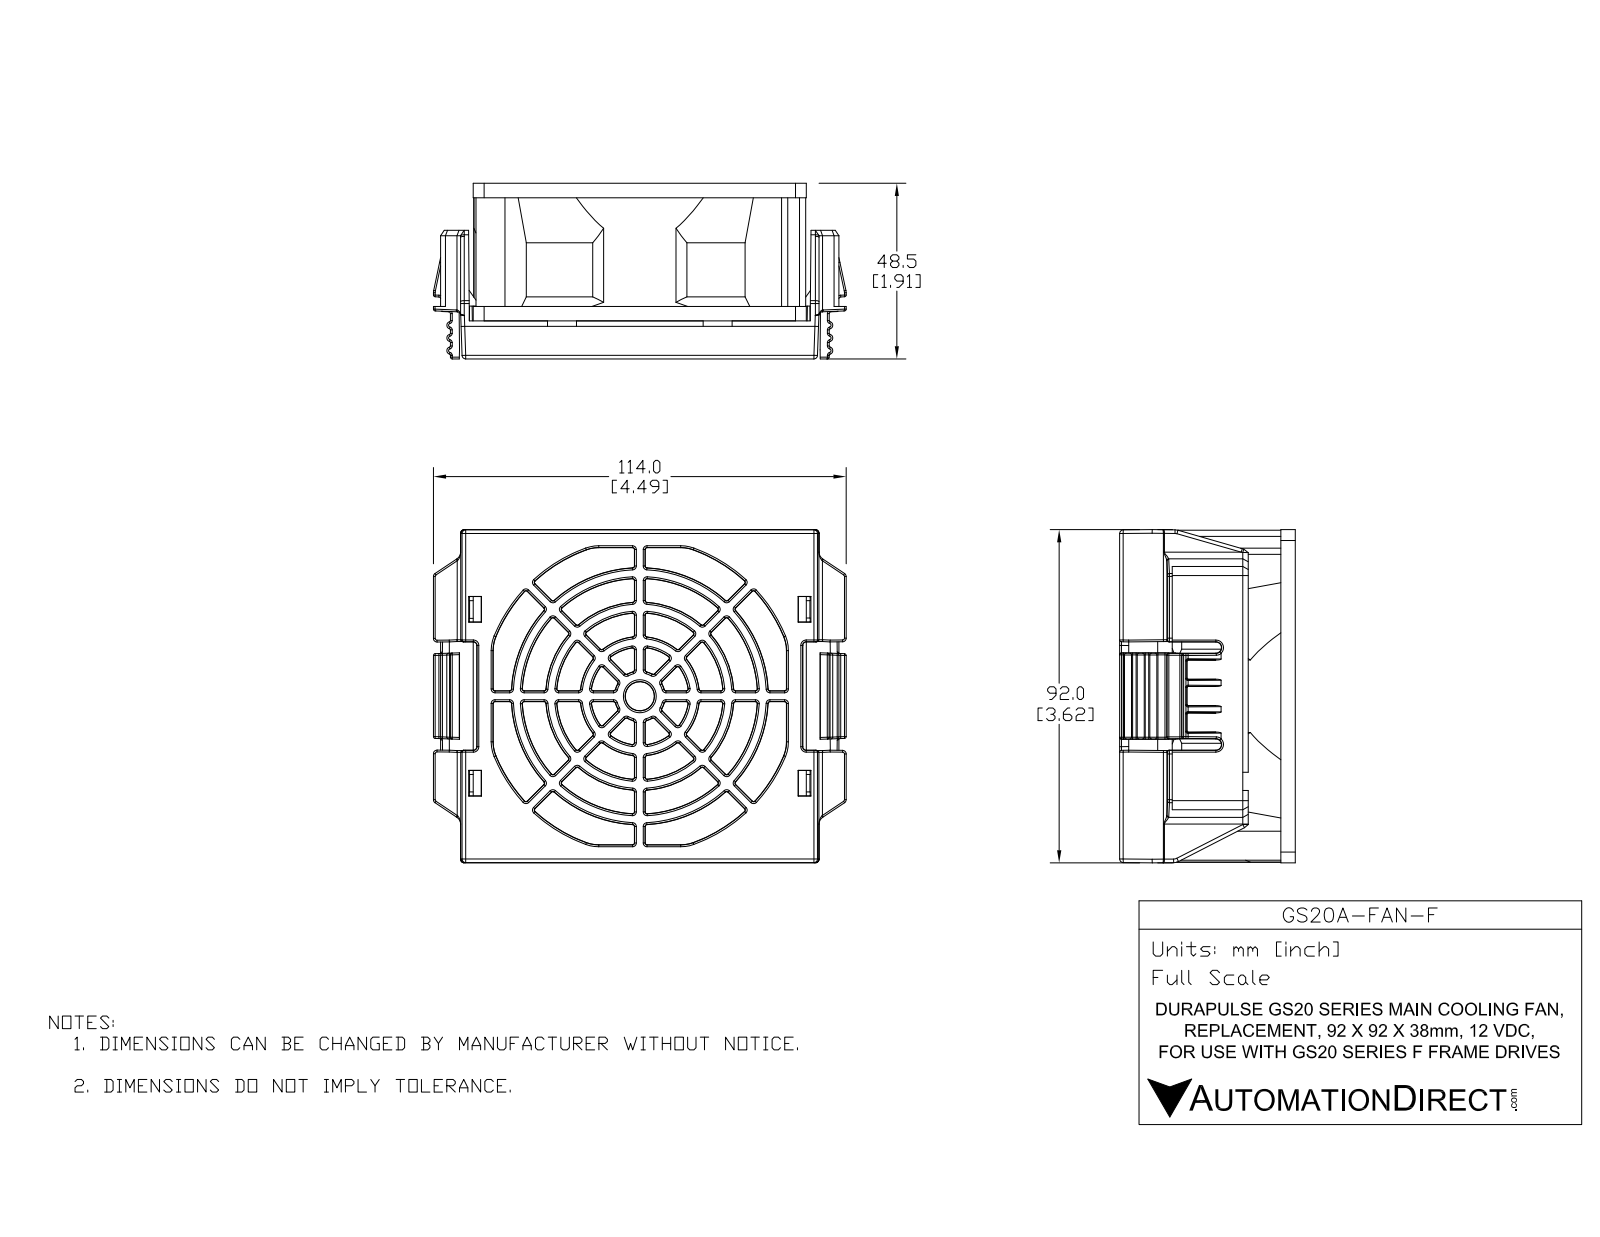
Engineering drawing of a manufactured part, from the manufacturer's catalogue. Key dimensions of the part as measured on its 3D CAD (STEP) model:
Part name (STEP PRODUCT): GS20A-FAN-F
STEP written by: SolidWorks 2017 (AUTOMOTIVE_DESIGN)
Units: inches
Bodies: 2 solids, 1822 faces (567 planar, 377 cylindrical, 878 other)
Overall size (bounding box): 4.488 × 3.622 × 1.909
Volume: 4.281 in³ · Surface area: 106 in²
Round holes (diameter × count): ⌀0.177 ×4, ⌀3.453 ×1
Round bosses / shafts (diameter × count): ⌀0.315 ×2
Partial cylindrical surfaces — rounded edges, fillets, slot ends (radius × count): R0.02 ×113, R0.039 ×48, R0.012 ×40, R0.118 ×12, R0.079 ×4, R0.087 ×4, R0.138 ×2, R1.805 ×1
Main face-to-face distances: 0.098, 3.614, 0.354, 0.075, 0.083, 3.539, 3.531, 0.157, 1.339, 0.315
Hole centre spacings: 2.297, 3.248, 4.593
